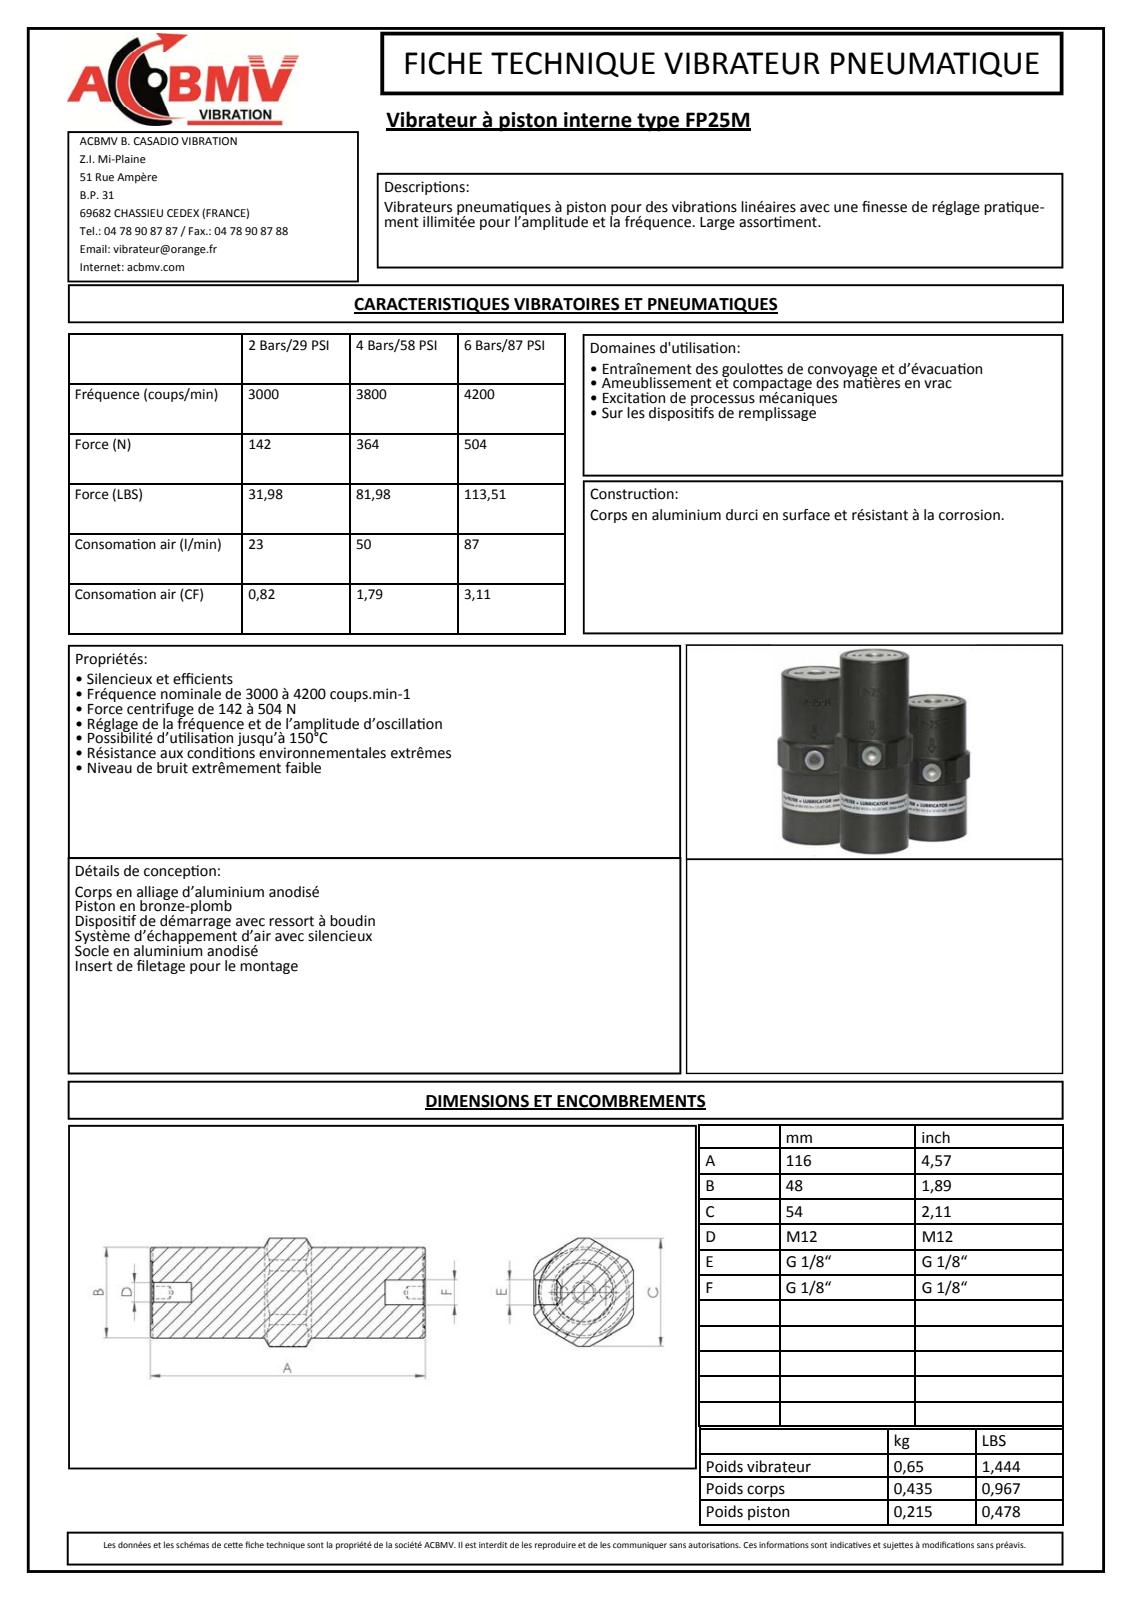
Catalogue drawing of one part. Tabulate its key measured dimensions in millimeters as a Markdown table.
| quantity | value |
| --- | --- |
| part name | 9025-20-M |
| STEP written by | Autodesk Inventor 2011 (CONFIG_CONTROL_DESIGN) |
| units | millimeters |
| bodies | 1 solid, 451 faces (184 planar, 57 cylindrical, 210 other) |
| overall size | 116 × 53.5 × 50 |
| volume | 210 535 mm³ |
| surface area | 23 706 mm² |
| round holes (diameter × count) | 6.2 × 4, 2.5 × 1, 8.57 × 1, 10.11 × 1, 11.45 × 1 |
| round bosses / shafts (diameter × count) | 48 × 1 |
| partial cylindrical surfaces (radius × count) | 14.5 × 1, 23.8 × 1, 24.08 × 1, 24.1 × 1, 26.75 × 1 |
| main face-to-face distances | 50, 116, 0.5, 115.5, 102.3, 101.8, 13.7, 18.5, 19, 83.3 |
| hole center spacings | 1, 11, 12, 23, 22, 24 |
